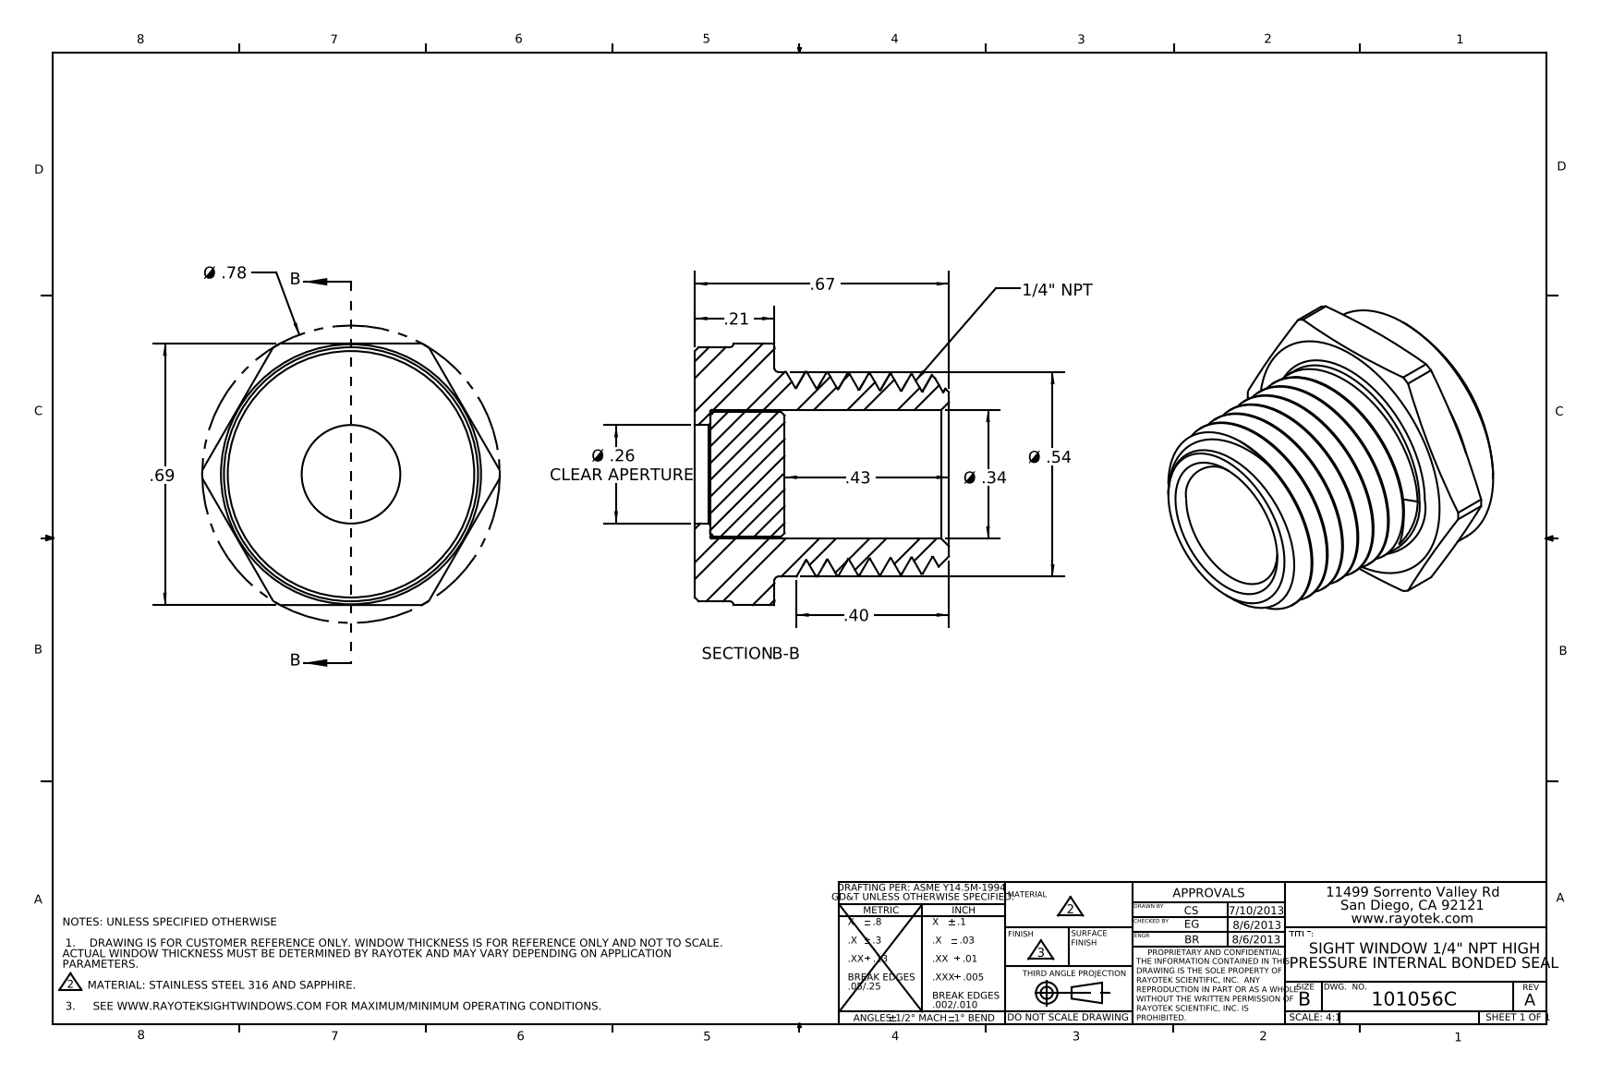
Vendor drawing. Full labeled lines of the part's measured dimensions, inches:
Part name (STEP PRODUCT): 101056; 402056; 403056
STEP written by: SolidWorks 2012 (AUTOMOTIVE_DESIGN)
Units: inches
Bodies: 2 solids, 72 faces (15 planar, 18 cylindrical, 39 other)
Overall size (bounding box): 0.785 × 0.69 × 0.67
Volume: 0.125 in³ · Surface area: 3.383 in²
Round holes (diameter × count): ⌀0.26 ×1, ⌀0.34 ×1
Round bosses / shafts (diameter × count): ⌀0.67 ×1, ⌀0.54 ×1, ⌀0.33 ×1
Partial cylindrical surfaces — rounded edges, fillets, slot ends (radius × count): R0.392 ×1
Main face-to-face distances: 0.69, 0.21, 0.04, 0.17, 0.237, 0.197, 0.027, 0.67, 0.63, 0.46
